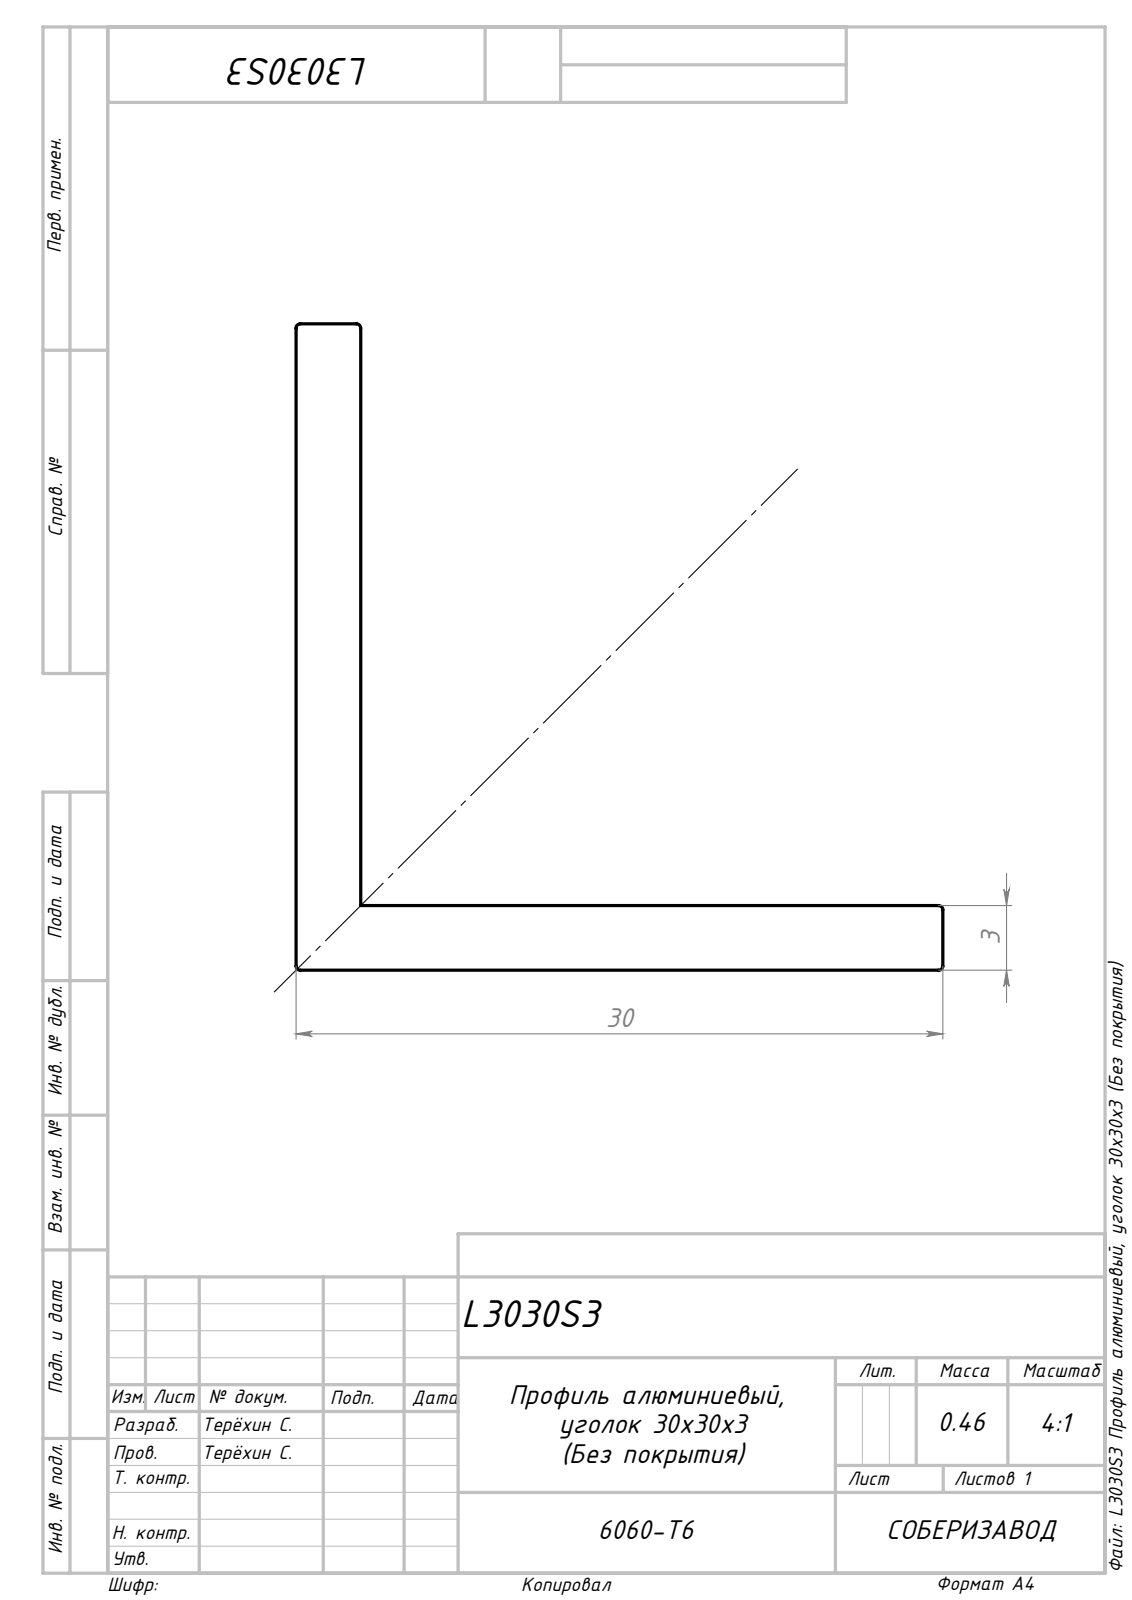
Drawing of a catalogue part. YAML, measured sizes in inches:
part_name: "Сборка6; L3030S3 Профиль алюминиевый, уголок 30x30x3 (Без покрытия)_00"
step_written_by: "SolidWorks 2024 (AUTOMOTIVE_DESIGN)"
units: inches
bodies: {solids: 1, faces: 13, planar: 8, cylindrical: 5, other: 0}
overall_size: [39.37, 1.181, 1.181]
volume: 10.43
surface_area: 185.9
partial_cylinders:
  - {radius: 0.008, count: 5}
face_to_face_distances: [0.118, 1.181, 1.063, 39.37]
